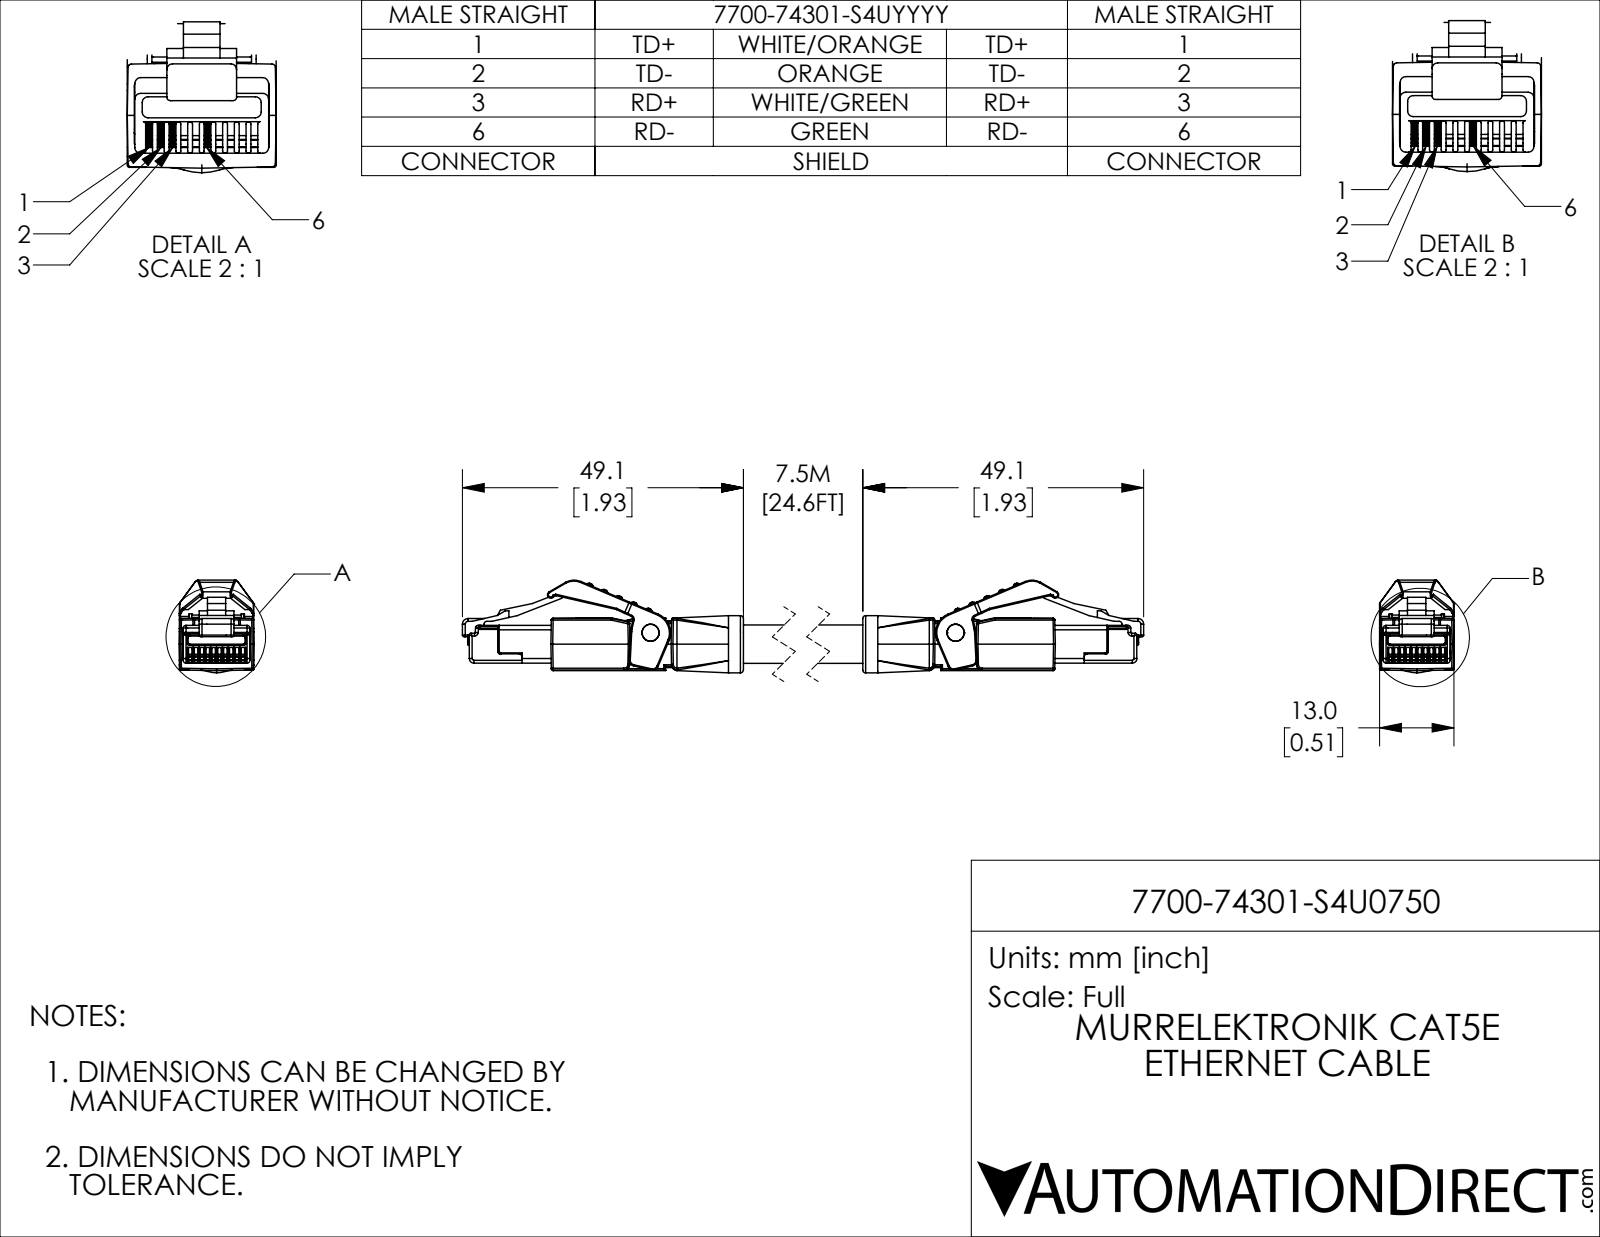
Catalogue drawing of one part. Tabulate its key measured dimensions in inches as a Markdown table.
| quantity | value |
| --- | --- |
| part name | 7700-74301-S4U0750; 7700-74301-S4U0750_1 |
| STEP written by | SolidWorks 2021 (CONFIG_CONTROL_DESIGN) |
| units | inches |
| bodies | 2 solids, 1406 faces (568 planar, 566 cylindrical, 272 other) |
| overall size | 5.112 × 0.638 × 0.512 |
| volume | 0.668 in³ |
| surface area | 10.82 in² |
| round holes (diameter × count) | 0.118 × 2 |
| round bosses / shafts (diameter × count) | 0.117 × 2, 0.394 × 1, 0.264 × 1 |
| partial cylindrical surfaces (radius × count) | 0.008 × 136, 0.012 × 114, 0.004 × 40, 0.02 × 36, 0.039 × 10, 0.031 × 6, 0.079 × 4, 0.197 × 4 |
| main face-to-face distances | 0.512, 0.362, 0.024, 0.488, 0.026, 0.26, 0.069, 0.443, 0.045, 0.419 |
| hole center spacings | 2.526 |
